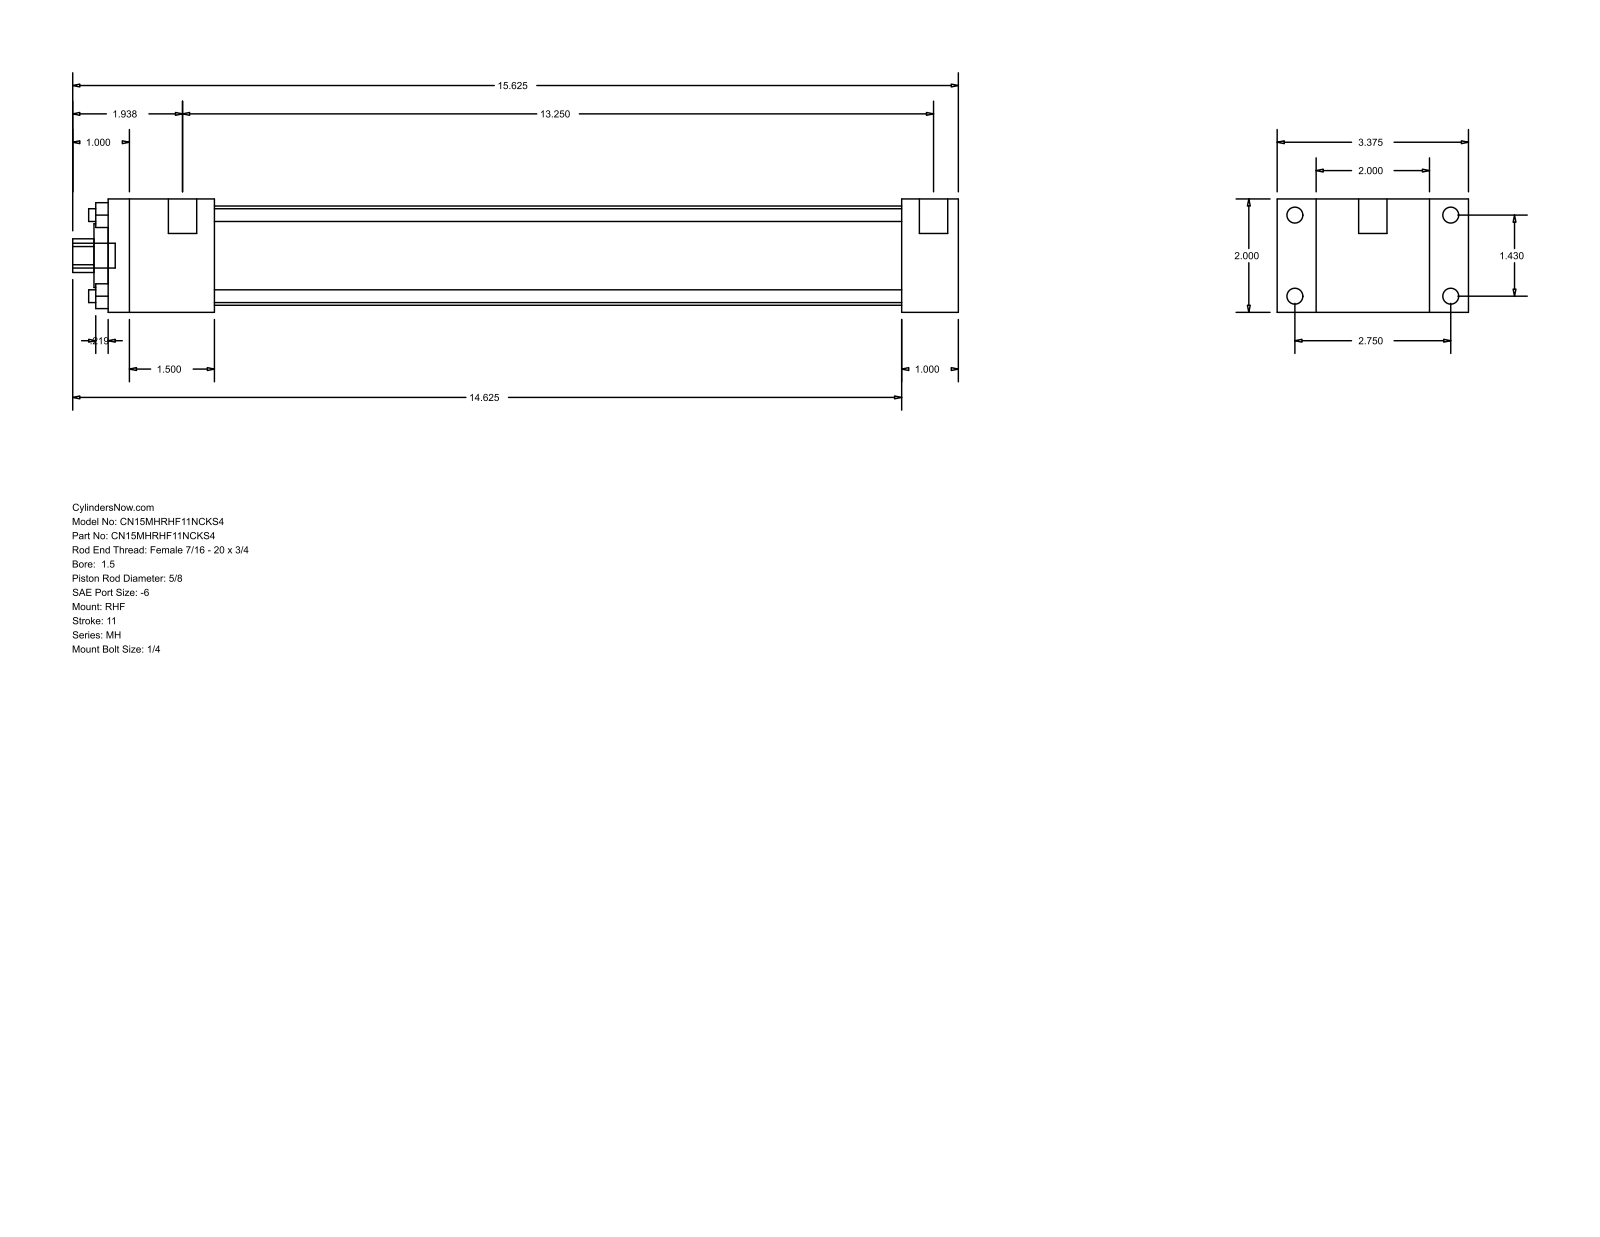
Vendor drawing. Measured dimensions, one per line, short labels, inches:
name: MH_RHF__0150_0.625
written by: GSSL Pune (CONFIG_CONTROL_DESIGN)
unit: in
bodies: 0 solids, 88 faces (60 planar, 28 cylindrical, 0 other)
size: 15.625 × 3.375 × 2
holes: 4× ⌀0.225, 1× ⌀0.625, 1× ⌀1.125, 1× ⌀1.75
bosses: 4× ⌀0.281, 4× ⌀0.219, 2× ⌀0.5, 1× ⌀0.437
rounds: 1× R0.297
face distances: 2, 0.687, 2.687, 1, 14, 15, 3.375, 1.875, 12.125, 13.125
hole spacings: 1.011, 1.43, 2.022
